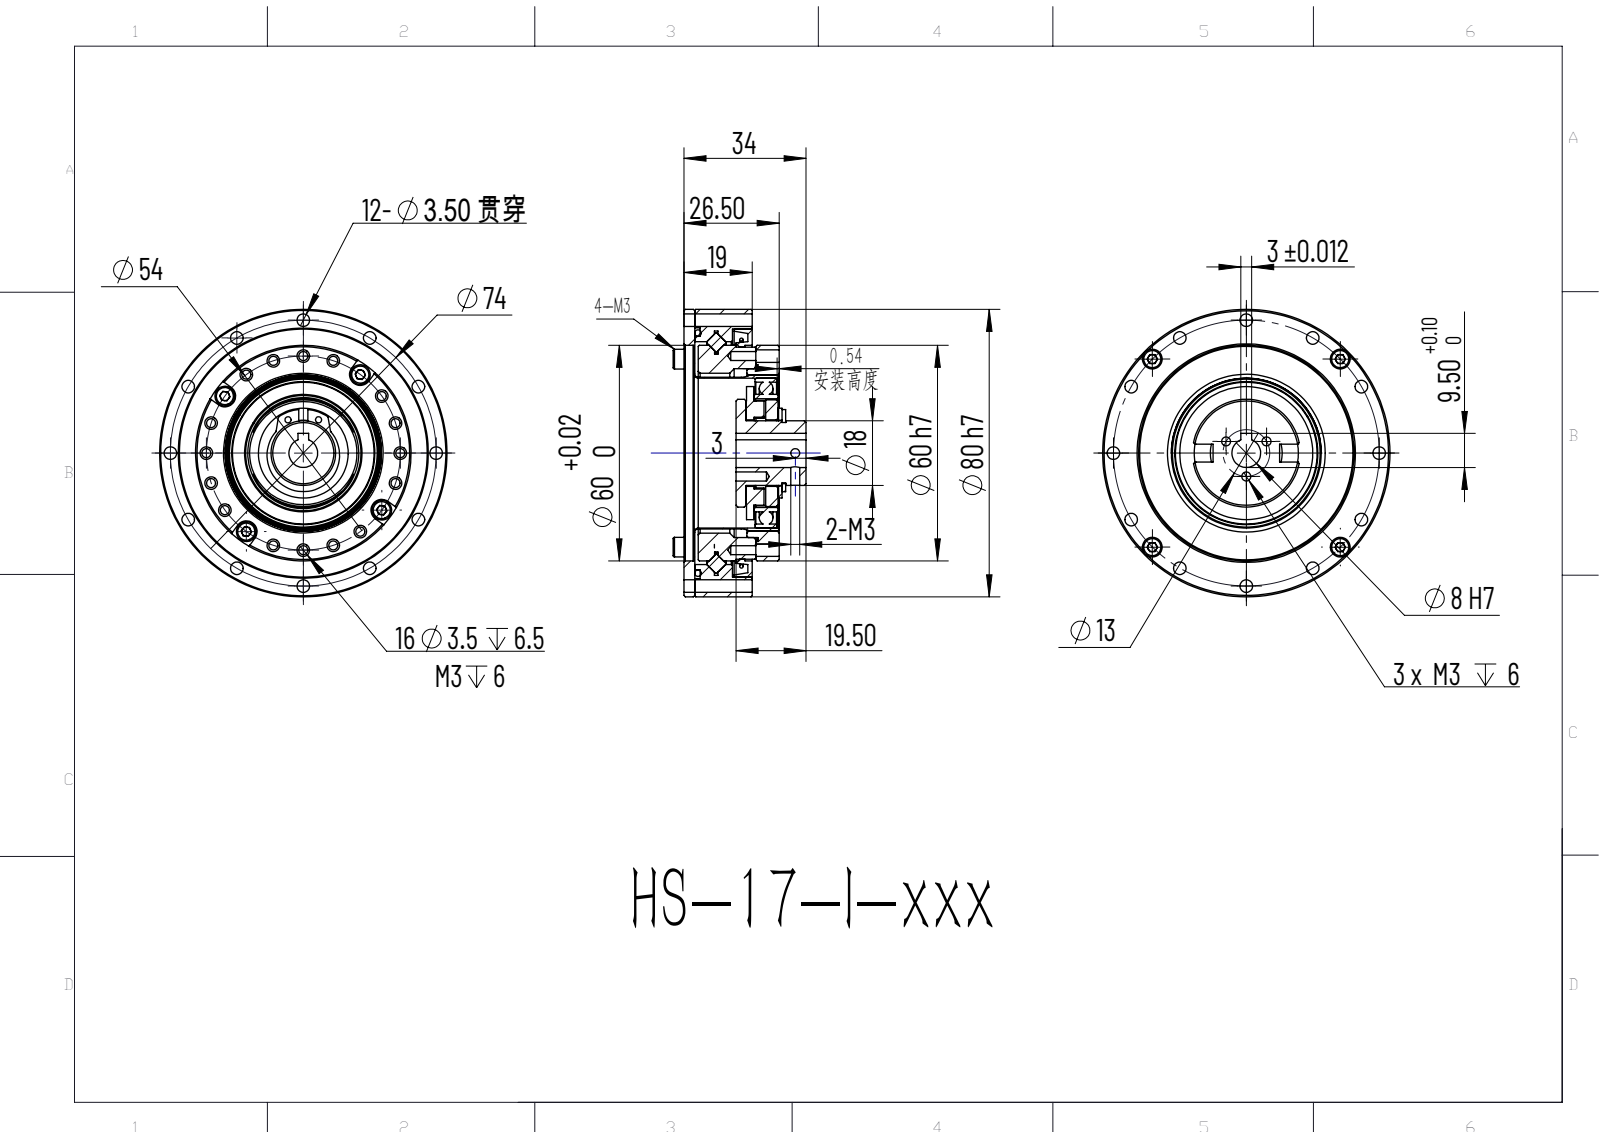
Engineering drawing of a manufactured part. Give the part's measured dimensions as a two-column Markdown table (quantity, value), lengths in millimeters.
| quantity | value |
| --- | --- |
| part name | HS-17-I; hexagon socket head cap screws gb_GB_FASTENER_SCREWS_HSHCS M3X8-C; ????-STXB-17080; 17-80??????_?? <1> (+8 more) |
| STEP written by | ONSHAPE BY PTC INC, 1.201 (AP242_MANAGED_MODEL_BASED_3D_ENGINEERING_MIM_LF) |
| units | millimeters |
| bodies | 96 solids, 2371 faces (934 planar, 1244 cylindrical, 193 other) |
| overall size | 80 × 80 × 37 |
| volume | 75 378 mm³ |
| surface area | 71 337 mm² |
| round holes (diameter × count) | 3.5 × 32, 2.5 × 29, 3.4 × 4, 1.7 × 2, 1.6 × 1, 2.4 × 1, 4.3 × 1, 8 × 1, 16.5 × 1, 18.3 × 1, 18.5 × 1, 30.3 × 1 |
| round bosses / shafts (diameter × count) | 4 × 36, 5.5 × 8, 3 × 8, 80 × 1, 65 × 1, 60 × 1, 55 × 1, 43.51 × 1 |
| partial cylindrical surfaces (radius × count) | 0.25 × 324, 0.35 × 324, 2.02 × 36, 3 × 4, 0.2 × 2, 0.5 × 2, 10 × 1, 10.1 × 1 |
| main face-to-face distances | 1, 16, 3, 10.5, 5.5, 6.5, 19, 4, 17, 4.5 |
| hole center spacings | 37, 52.33, 27, 19.15, 37.01, 9.66, 31.74, 45.8 |
